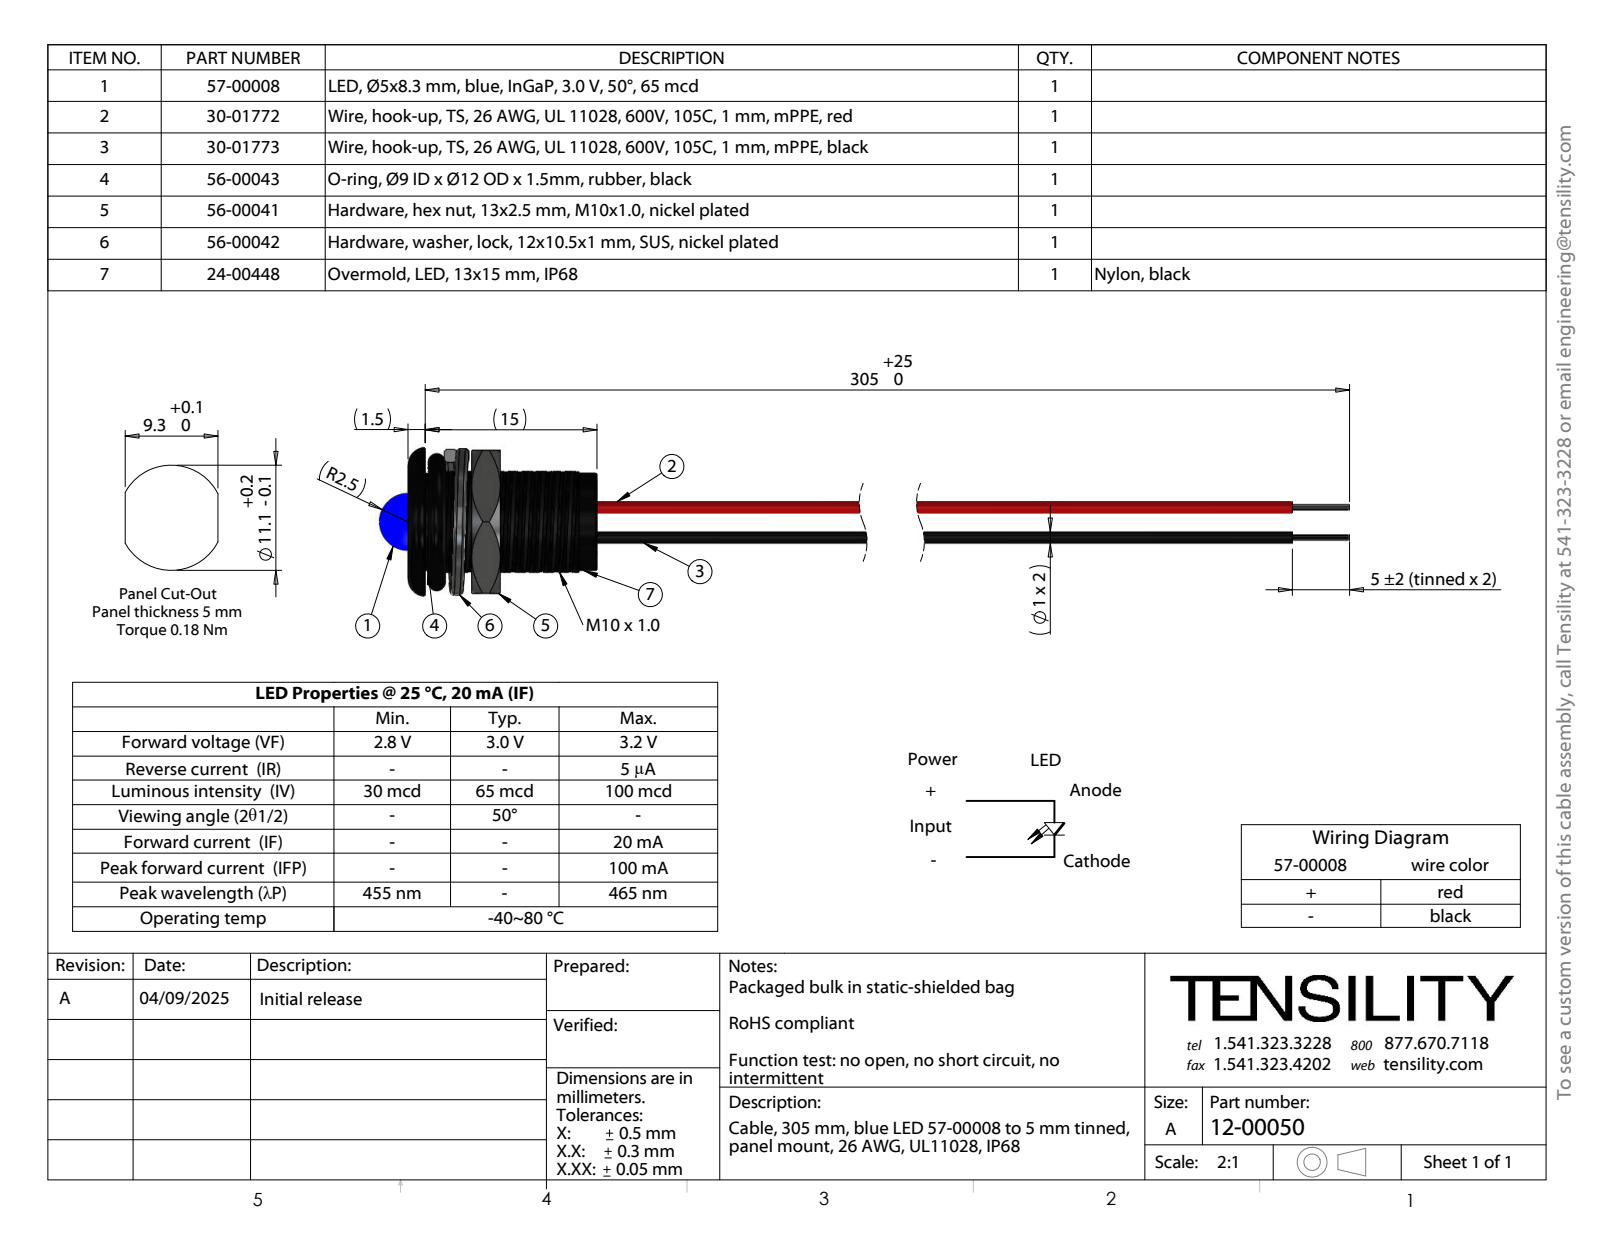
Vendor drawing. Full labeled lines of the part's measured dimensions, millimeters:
Part name (STEP PRODUCT): 24-00448; 57-00008_trimmed leads; 56-00041; 30-01772_stripped and tinned (+4 more)
STEP written by: SolidWorks 2021 (CONFIG_CONTROL_DESIGN)
Units: millimetres
Bodies: 57 solids, 514 faces (185 planar, 246 cylindrical, 83 other)
Overall size (bounding box): 173.99 × 14.43 × 12.99
Volume: 1 769 mm³ · Surface area: 6 568 mm²
Round holes (diameter × count): ⌀1 ×2
Round bosses / shafts (diameter × count): ⌀1 ×2, ⌀0.83 ×2, ⌀8.5 ×1, ⌀5 ×1
Partial cylindrical surfaces — rounded edges, fillets, slot ends (radius × count): R4.33 ×1, R5 ×1
Main face-to-face distances: 1.5, 16.5, 15, 12.5, 8.06, 6.56, 8.44, 5.56, 4.06, 2.5
Hole centre spacings: 0.36, 0.38, 0.33, 2.43, 2.35, 2.48, 2.52, 2.56
